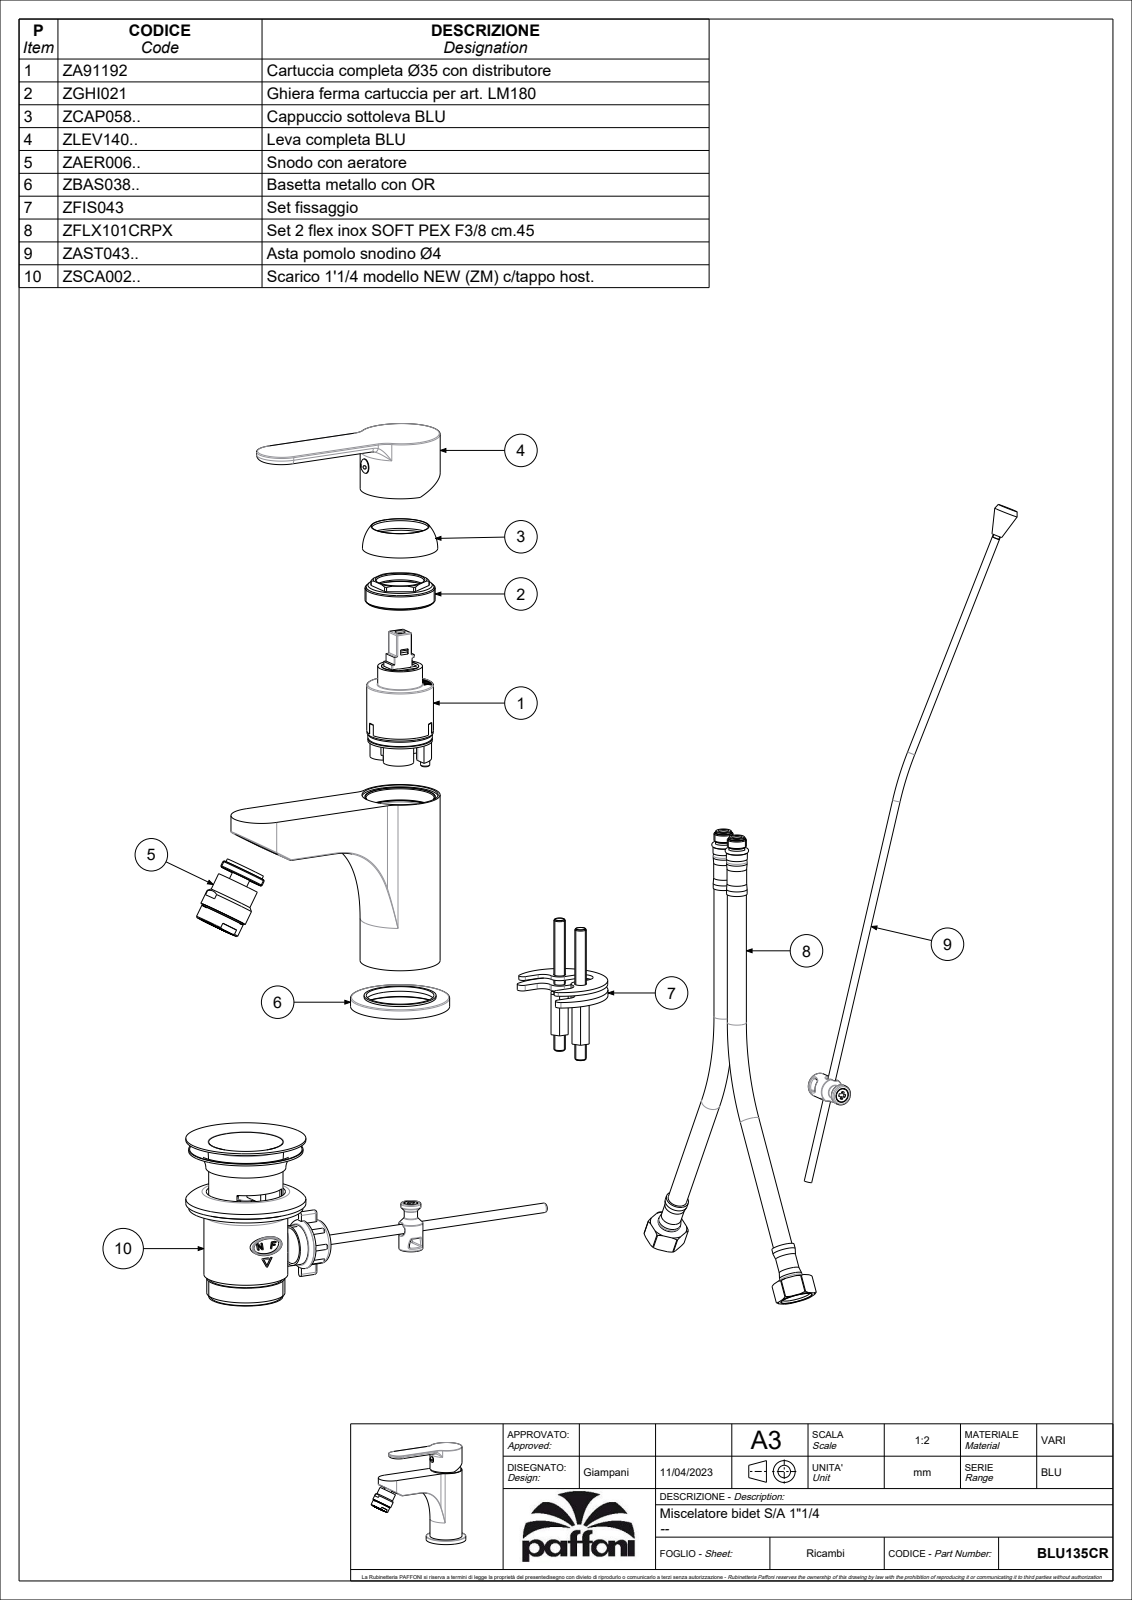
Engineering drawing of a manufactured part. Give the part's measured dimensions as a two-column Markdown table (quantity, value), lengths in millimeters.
| quantity | value |
| --- | --- |
| part name | BLU135CR |
| STEP written by | CREO PARAMETRIC BY PTC INC, 2020044 (CONFIG_CONTROL_DESIGN) |
| units | millimeters |
| bodies | 3 solids, 2699 faces (1921 planar, 473 cylindrical, 305 other) |
| overall size | 148.31 × 126.7 × 52 |
| volume | 131 091 mm³ |
| surface area | 95 062 mm² |
| round holes (diameter × count) | 5 × 4, 8 × 3, 9 × 3, 12 × 3, 6 × 2, 6.5 × 2, 3 × 1, 3.3 × 1, 3.5 × 1, 4 × 1, 4.6 × 1, 5.5 × 1 |
| round bosses / shafts (diameter × count) | 10 × 3, 14 × 2, 12 × 2, 11 × 2, 10.5 × 2, 6 × 2, 5 × 2, 4.8 × 2 |
| partial cylindrical surfaces (radius × count) | 0.5 × 70, 1.5 × 23, 0.3 × 20, 0.54 × 14, 3 × 14, 1 × 13, 1.2 × 9, 10 × 4 |
| main face-to-face distances | 3, 29.5, 1, 32.5, 2.7, 5, 3.5, 27, 95.2, 29.7 |
| hole center spacings | 13.6, 0.71, 2.83, 8.51, 8.6, 9.66, 9.85, 11.18 |
